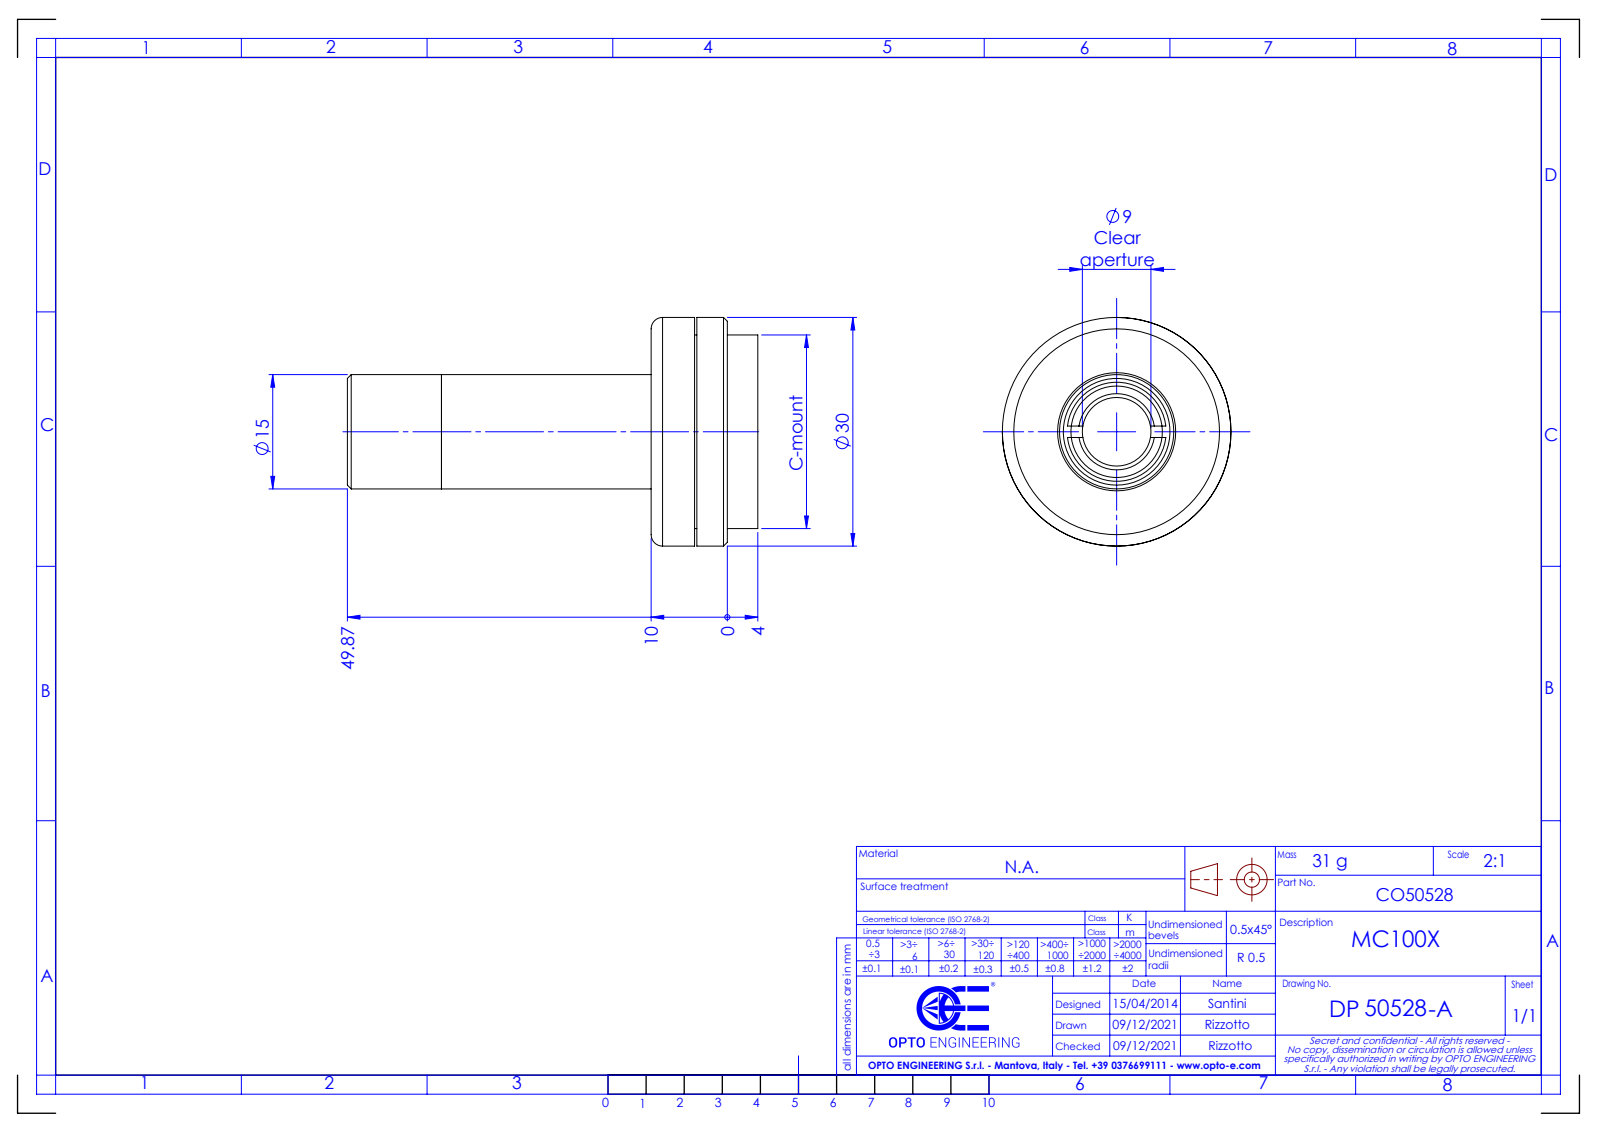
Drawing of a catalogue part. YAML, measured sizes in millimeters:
part_name: "DP50528-A_MC100X"
step_written_by: "SolidWorks 2021 (CONFIG_CONTROL_DESIGN)"
units: millimeters
bodies: {solids: 0, faces: 48, planar: 15, cylindrical: 18, other: 15}
overall_size: [53.87, 30, 30]
round_holes:
  - {diameter: 9, count: 1}
  - {diameter: 12, count: 1}
round_bosses_or_shafts:
  - {diameter: 30, count: 1}
  - {diameter: 25.4, count: 1}
  - {diameter: 15, count: 1}
  - {diameter: 14.5, count: 1}
face_to_face_distances: [4, 6, 5.7, 10, 4.3, 14, 8.3, 8, 39.87, 45.57]
